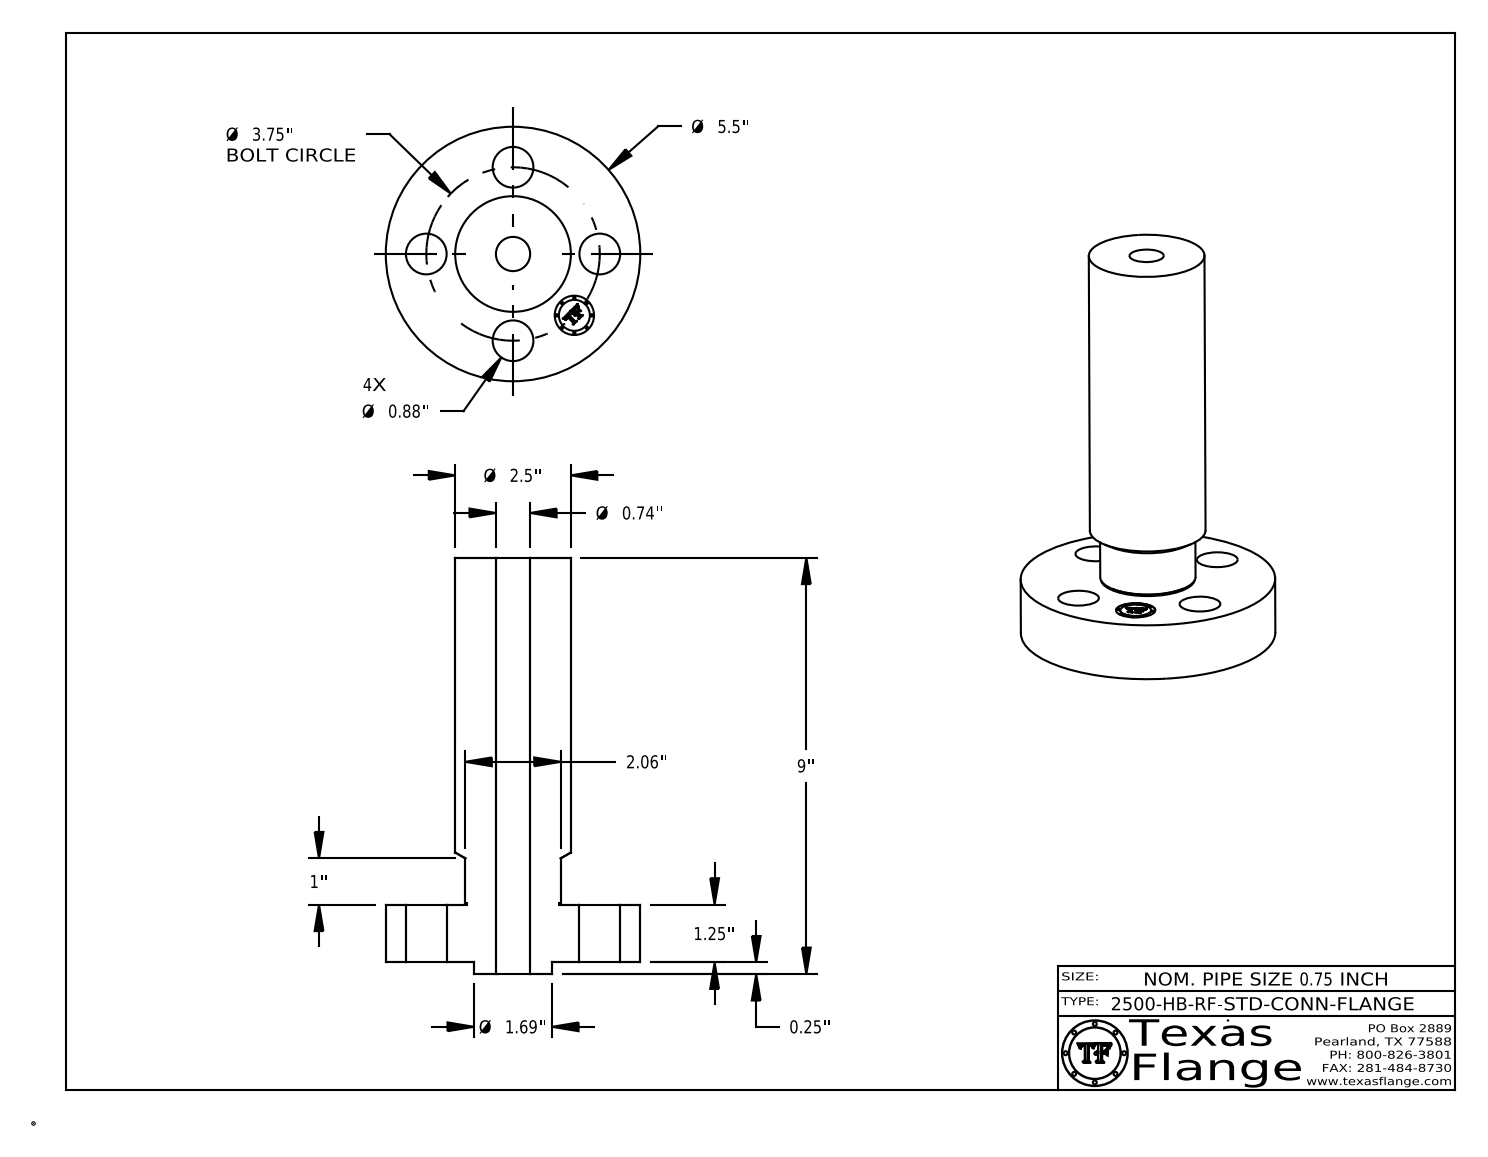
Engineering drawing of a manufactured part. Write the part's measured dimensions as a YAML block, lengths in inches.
part_name: "0.75-2500-HB-RF-STD-CONN-FLANGE"
step_written_by: "CATIA V5 STEP AP214 (AUTOMOTIVE_DESIGN)"
units: inches
bodies: {solids: 1, faces: 413, planar: 369, cylindrical: 38, other: 6}
overall_size: [9, 5.5, 5.5]
volume: 58.48
surface_area: 159.7
round_holes:
  - {diameter: 0.88, count: 4}
  - {diameter: 0.74, count: 1}
  - {diameter: 0.85, count: 1}
round_bosses_or_shafts:
  - {diameter: 0.051, count: 8}
  - {diameter: 5.5, count: 1}
  - {diameter: 2.5, count: 1}
  - {diameter: 2.06, count: 1}
  - {diameter: 1.69, count: 1}
  - {diameter: 0.67, count: 1}
face_to_face_distances: [1.25, 8.75, 7.5, 0.25, 1.5, 9, 1.495, 1.245, 7.505, 0.254]
hole_center_spacings: [1.875, 2.652, 1.435, 3.465, 3.75]
